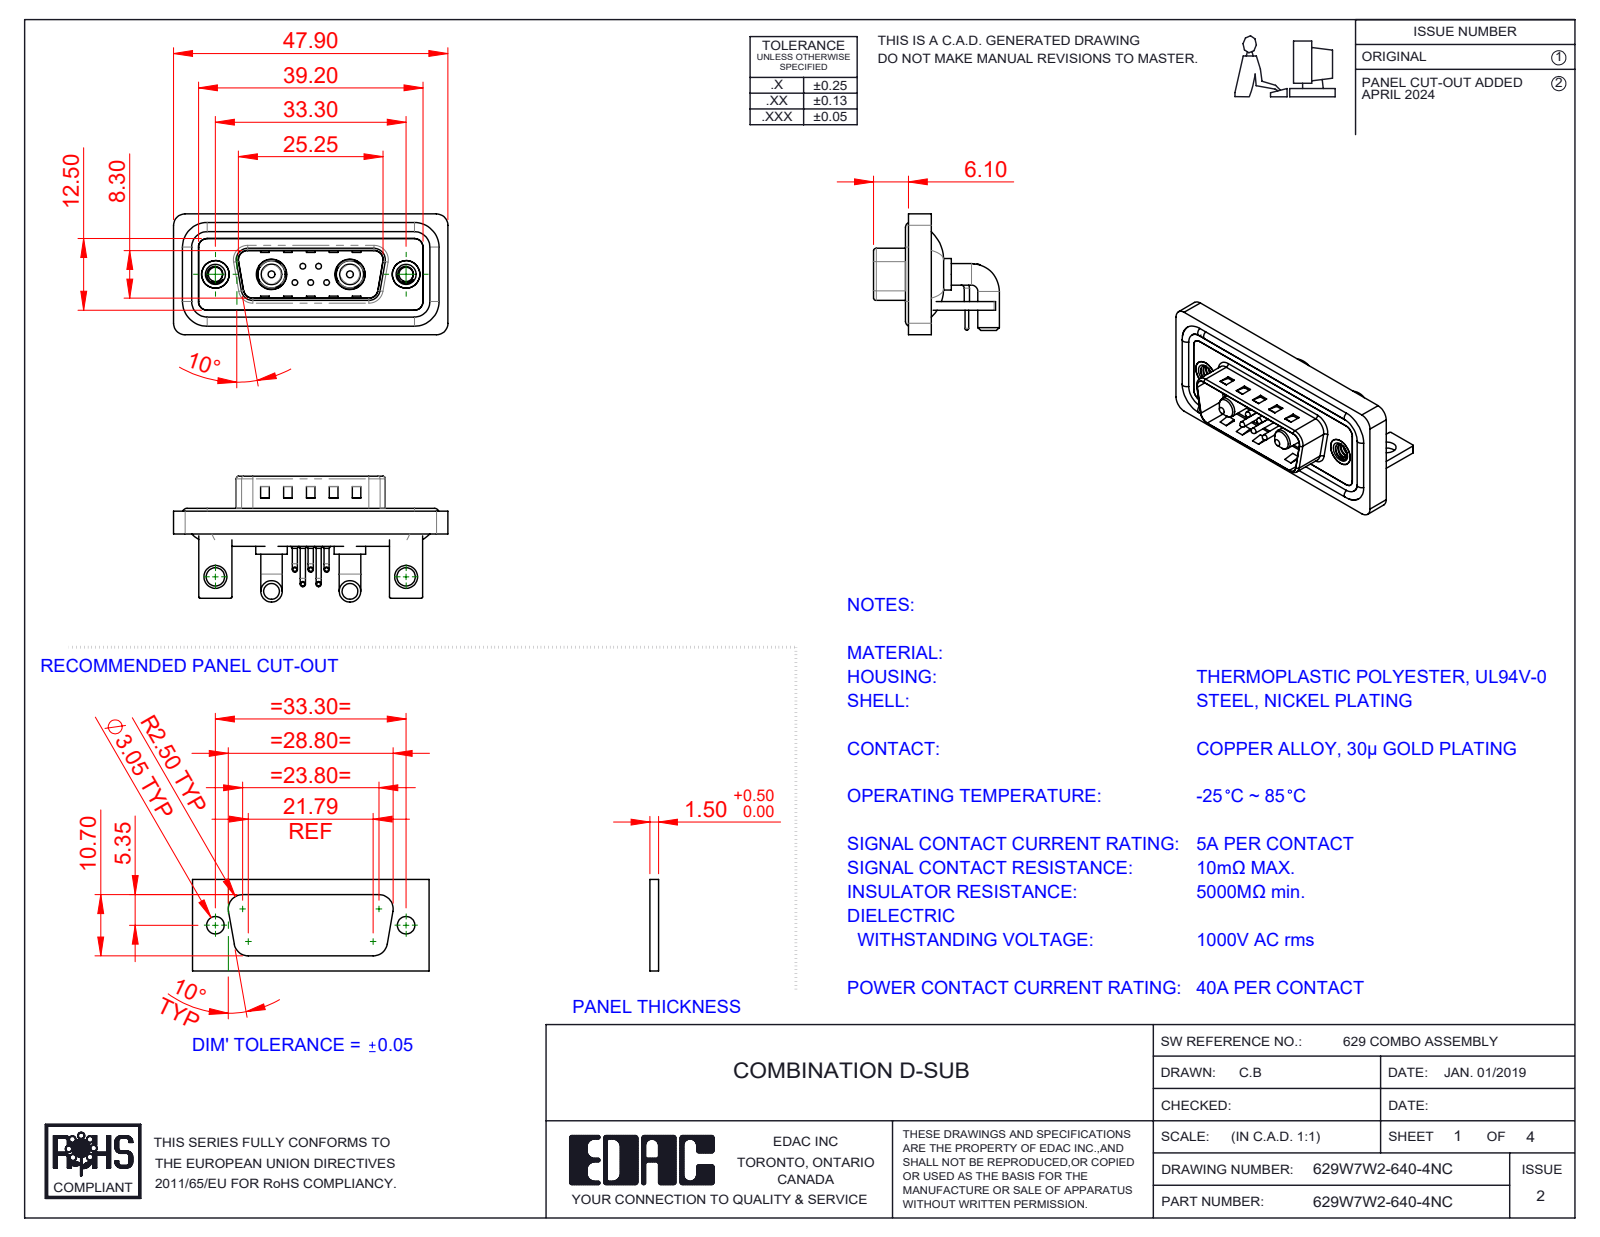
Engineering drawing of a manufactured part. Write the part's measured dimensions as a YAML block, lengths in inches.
part_name: "629Combo Contact Row 1; 629Combo Stabilizer Bracket; 629W7W2-640-4NC; 629Combo Waterproof Housing_15 Contacts (+6 more)"
step_written_by: "SolidWorks 2023 (CONFIG_CONTROL_DESIGN)"
units: inches
bodies: {solids: 18, faces: 1121, planar: 537, cylindrical: 424, other: 160}
overall_size: [1.886, 0.865, 0.831]
volume: 0.372
surface_area: 15.22
round_holes:
  - {diameter: 0.03, count: 5}
  - {diameter: 0.063, count: 5}
  - {diameter: 0.079, count: 5}
  - {diameter: 0.098, count: 2}
  - {diameter: 0.126, count: 2}
  - {diameter: 0.157, count: 2}
  - {diameter: 0.189, count: 2}
  - {diameter: 0.191, count: 2}
  - {diameter: 0.197, count: 2}
  - {diameter: 0.209, count: 2}
round_bosses_or_shafts:
  - {diameter: 0.035, count: 10}
  - {diameter: 0.059, count: 5}
  - {diameter: 0.039, count: 5}
  - {diameter: 0.026, count: 5}
  - {diameter: 0.148, count: 4}
  - {diameter: 0.063, count: 4}
  - {diameter: 0.217, count: 2}
  - {diameter: 0.205, count: 2}
partial_cylinders:
  - {radius: 0.079, count: 21}
  - {radius: 0.059, count: 18}
  - {radius: 0.01, count: 16}
  - {radius: 0.02, count: 9}
  - {radius: 0.063, count: 8}
  - {radius: 0.04, count: 5}
  - {radius: 0.024, count: 4}
  - {radius: 0.026, count: 4}
face_to_face_distances: [0.016, 0.059, 0.031, 0.114, 0.083, 0.043, 0.063, 0.047, 0.146, 0.177]
hole_center_spacings: [0.124, 0.109, 0.386, 0.925, 1.311, 0.17, 0.17, 0.198]
